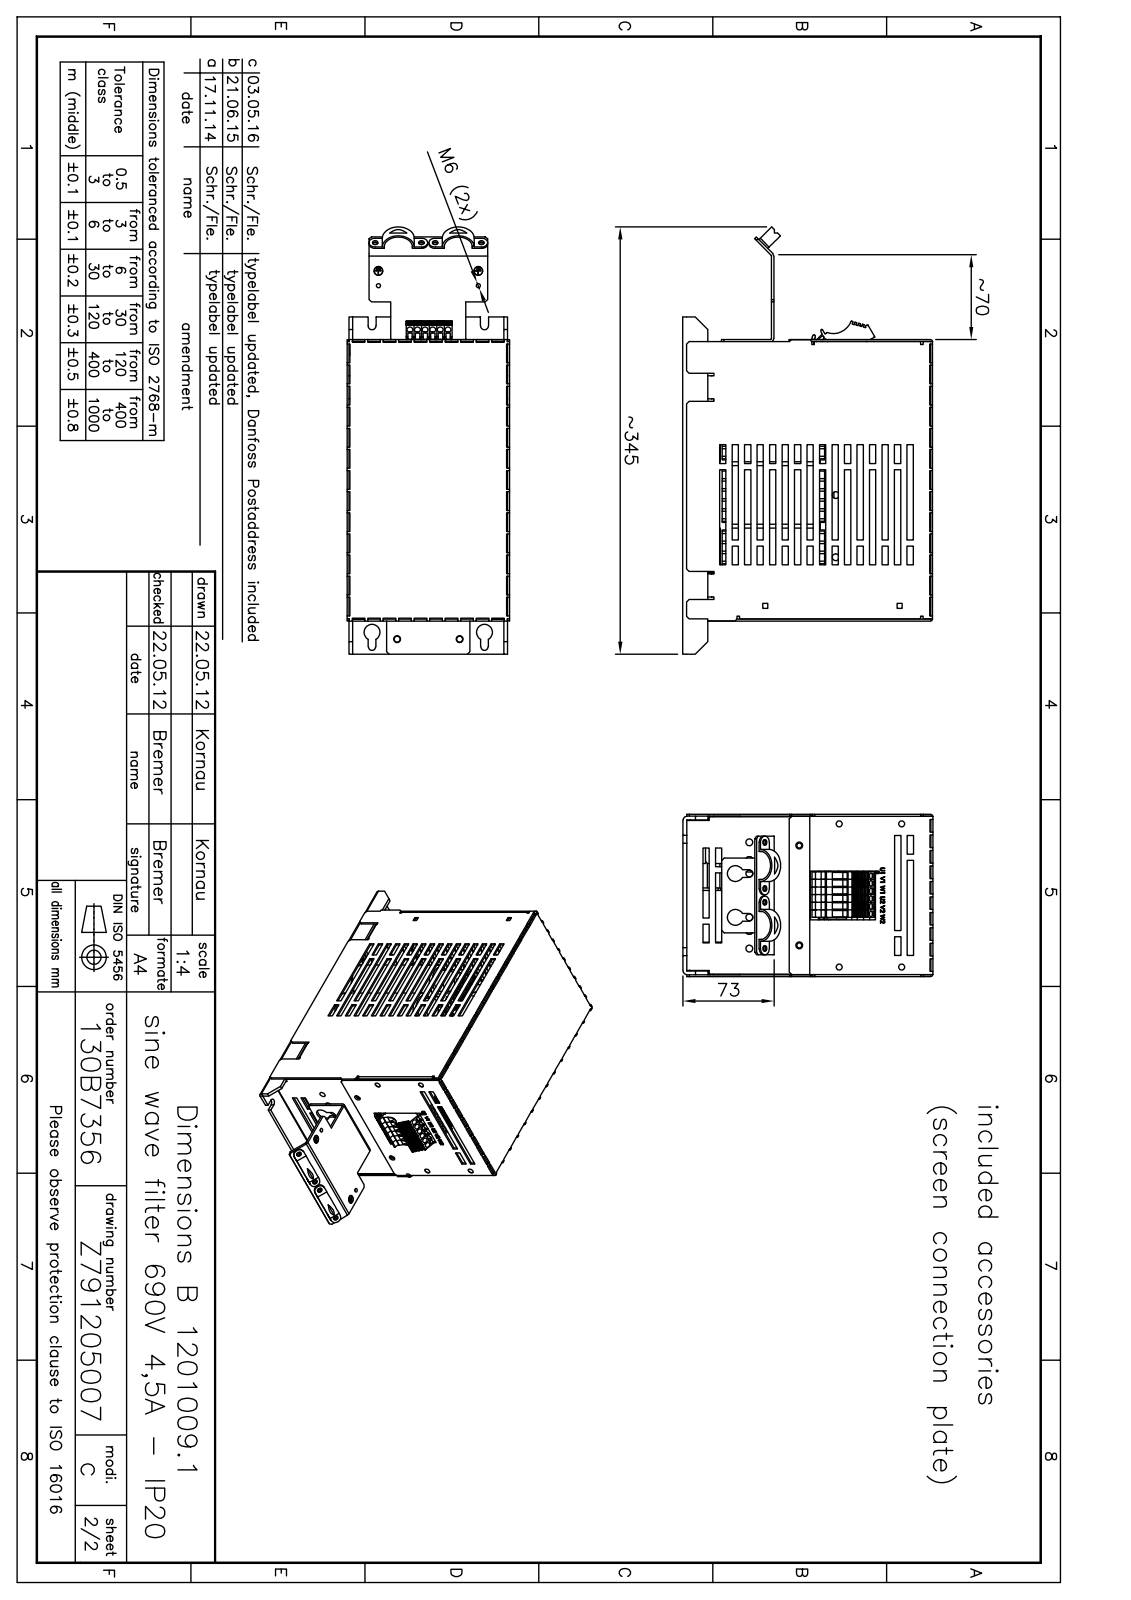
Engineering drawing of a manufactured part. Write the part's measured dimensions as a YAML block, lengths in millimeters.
part_name: "countersunk flat head cross recess screw_din_ISO 7046-1 - M6 x 10 - Z --- 10N; D55; pan head cross recess screw_din_ISO 7045 - M6 x 16 - Z --- 16N; #060-0492 (+8 more)"
step_written_by: "SolidWorks 2014 (AUTOMOTIVE_DESIGN)"
units: millimeters
bodies: {solids: 105, faces: 5712, planar: 3866, cylindrical: 1436, other: 410}
overall_size: [342.63, 200, 130]
volume: 1666000
surface_area: 860576
round_holes:
  - {diameter: 5.5, count: 20}
  - {diameter: 5, count: 15}
  - {diameter: 4.2, count: 12}
  - {diameter: 4.72, count: 12}
  - {diameter: 4.3, count: 9}
  - {diameter: 5.3, count: 8}
  - {diameter: 7, count: 6}
  - {diameter: 3.3, count: 5}
  - {diameter: 4, count: 5}
  - {diameter: 6.4, count: 5}
  - {diameter: 8.5, count: 5}
  - {diameter: 3.7, count: 4}
round_bosses_or_shafts:
  - {diameter: 10, count: 12}
  - {diameter: 9, count: 9}
  - {diameter: 7, count: 9}
  - {diameter: 9.3, count: 6}
  - {diameter: 5, count: 6}
  - {diameter: 9.5, count: 4}
  - {diameter: 8.5, count: 4}
  - {diameter: 6.95, count: 4}
partial_cylinders:
  - {radius: 2, count: 68}
  - {radius: 0.2, count: 36}
  - {radius: 0.5, count: 35}
  - {radius: 0.1, count: 34}
  - {radius: 0.49, count: 24}
  - {radius: 1.6, count: 15}
  - {radius: 1, count: 14}
  - {radius: 2.9, count: 14}
face_to_face_distances: [1.5, 128.5, 2, 127, 3, 50, 100, 10, 130, 2.3]
hole_center_spacings: [6.1, 24.81, 50, 12.2, 26.97, 37, 48, 11]
